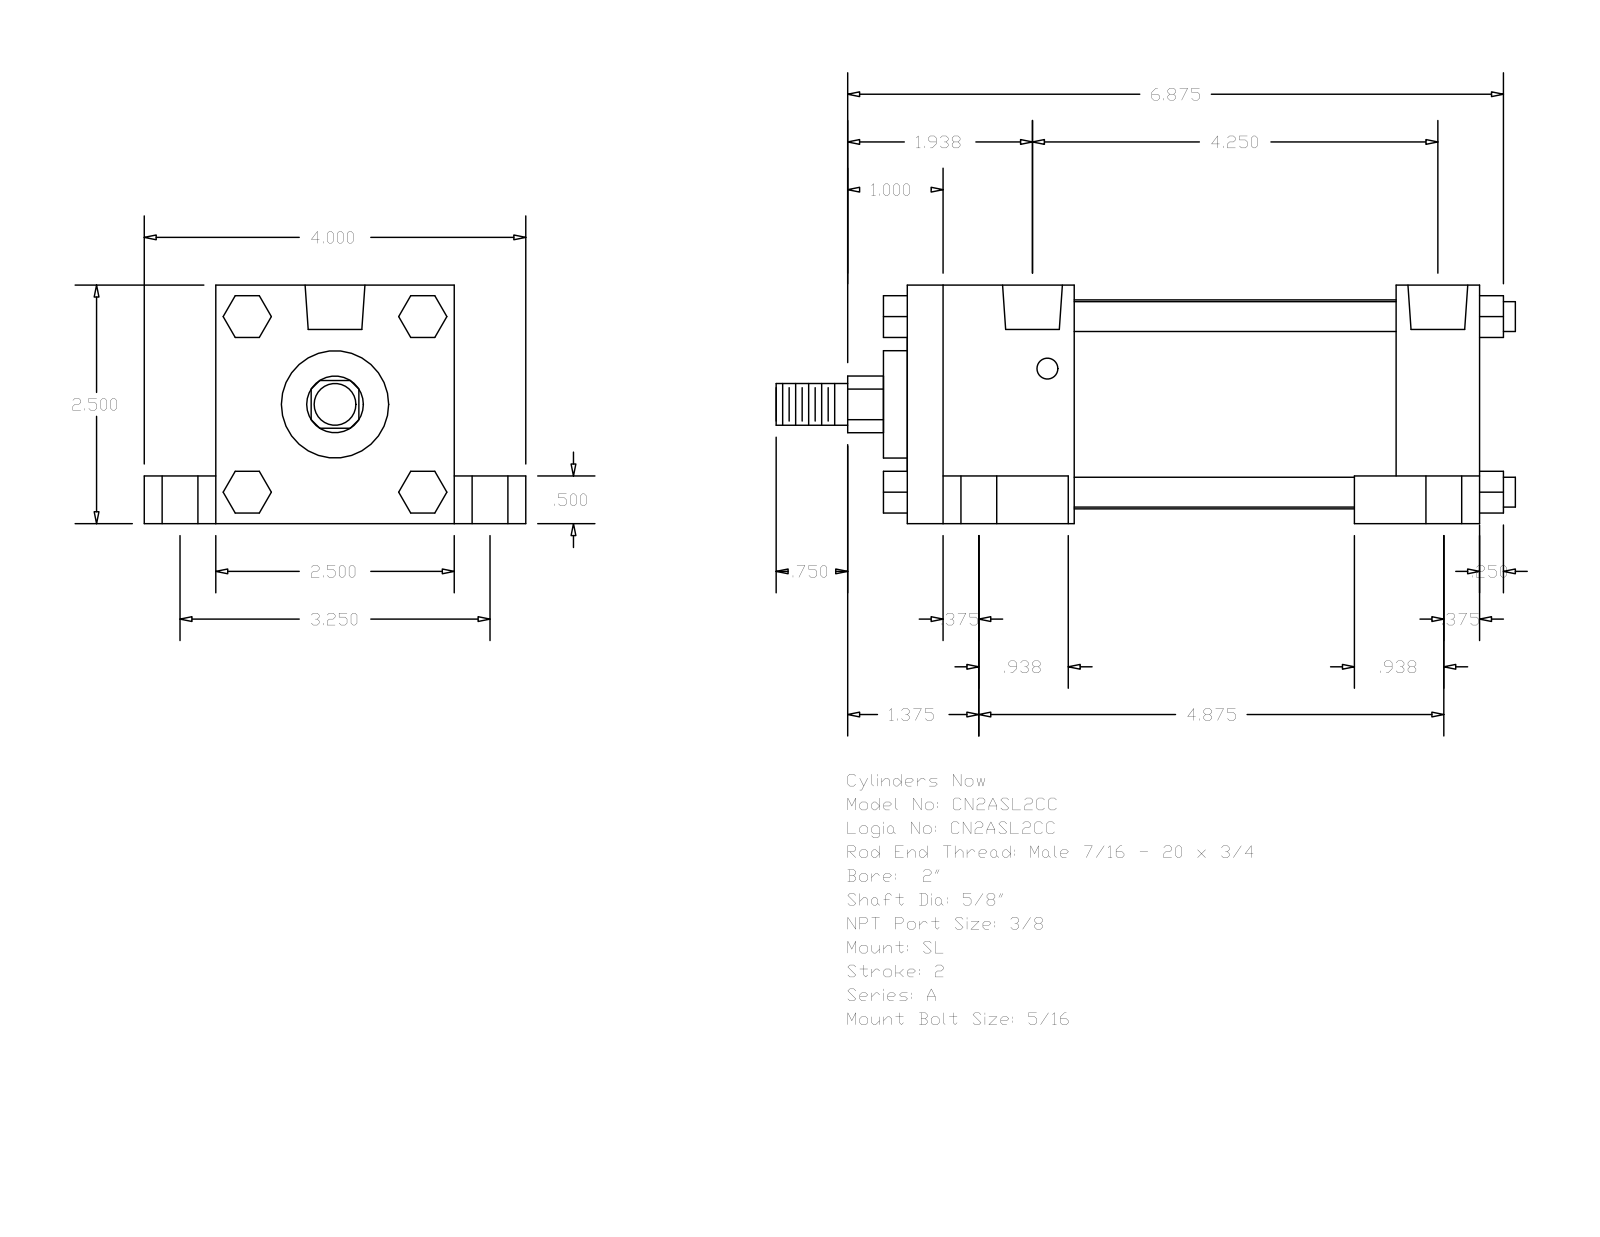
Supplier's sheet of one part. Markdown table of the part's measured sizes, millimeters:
| quantity | value |
| --- | --- |
| part name | A_SL__0200_0.625 |
| STEP written by | GSSL Pune (CONFIG_CONTROL_DESIGN) |
| units | millimeters |
| bodies | 0 solids, 148 faces (112 planar, 36 cylindrical, 0 other) |
| overall size | 196.85 × 101.6 × 63.5 |
| round holes (diameter × count) | 5.56 × 4, 9.53 × 4, 15.88 × 4, 15.93 × 2 |
| round bosses / shafts (diameter × count) | 7.94 × 4, 55.63 × 1, 28.57 × 1, 15.88 × 1, 11.11 × 1 |
| partial cylindrical surfaces (radius × count) | 7.54 × 1 |
| main face-to-face distances | 63.5, 152.4, 50.8, 12.7, 19.05, 82.55, 44.45, 107.95, 130.17, 85.72 |
| hole center spacings | 41.3, 41.64, 43.67, 45.13, 82.54, 100, 113.34, 117.06 |
